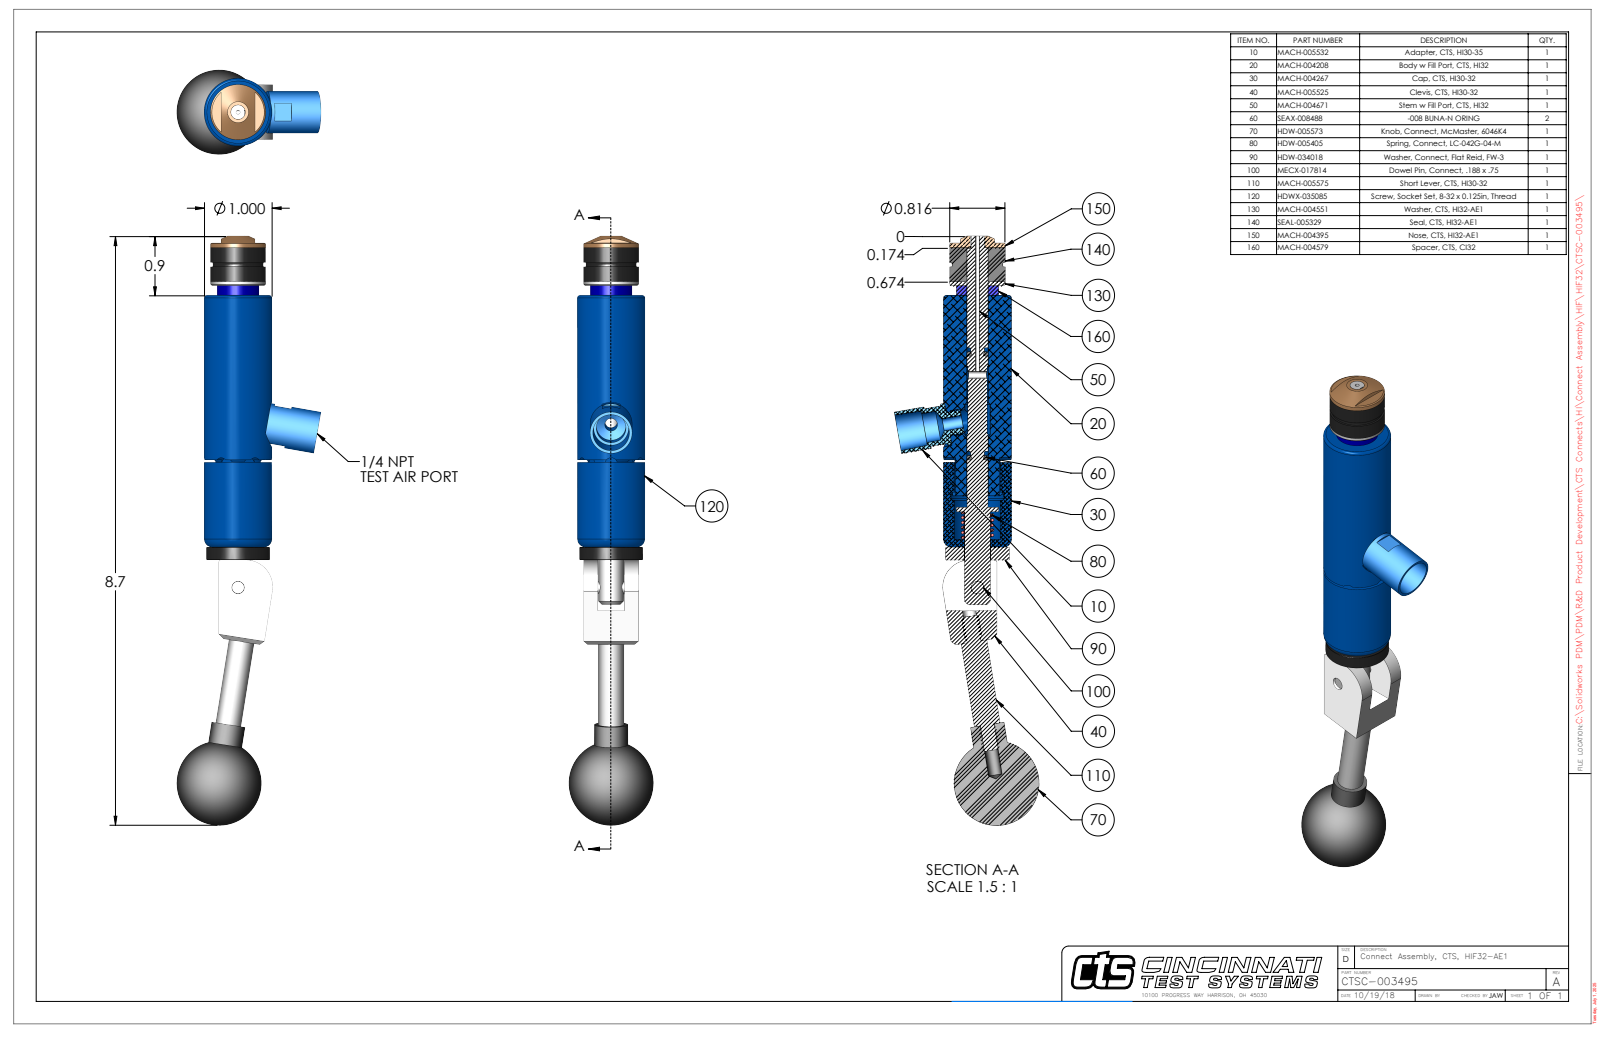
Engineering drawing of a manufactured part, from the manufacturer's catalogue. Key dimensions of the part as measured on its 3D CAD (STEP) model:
Part name (STEP PRODUCT): CTSC-003495
STEP written by: SolidWorks 2023 (AUTOMOTIVE_DESIGN)
Units: inches
Bodies: 10 solids, 286 faces (99 planar, 123 cylindrical, 64 other)
Overall size (bounding box): 8.704 × 2.128 × 1.25
Volume: 5.248 in³ · Surface area: 42.52 in²
Round holes (diameter × count): ⌀0.201 ×2, ⌀0.063 ×1, ⌀0.109 ×1, ⌀0.136 ×1, ⌀0.15 ×1, ⌀0.187 ×1, ⌀0.189 ×1, ⌀0.213 ×1, ⌀0.31 ×1, ⌀0.314 ×1, ⌀0.316 ×1, ⌀0.385 ×1
Round bosses / shafts (diameter × count): ⌀0.25 ×2, ⌀0.201 ×2, ⌀1 ×1, ⌀0.936 ×1, ⌀0.816 ×1, ⌀0.62 ×1, ⌀0.618 ×1, ⌀0.5 ×1
Partial cylindrical surfaces — rounded edges, fillets, slot ends (radius × count): R0.093 ×6, R0.029 ×2, R0.066 ×1, R0.325 ×1, R0.4 ×1, R0.454 ×1
Main face-to-face distances: 0.21, 0.602, 0.5, 4.42, 3.92, 0.702, 0.202, 3.719, 0.812, 4.608
Hole centre spacings: 0.599, 1.658, 2.252
